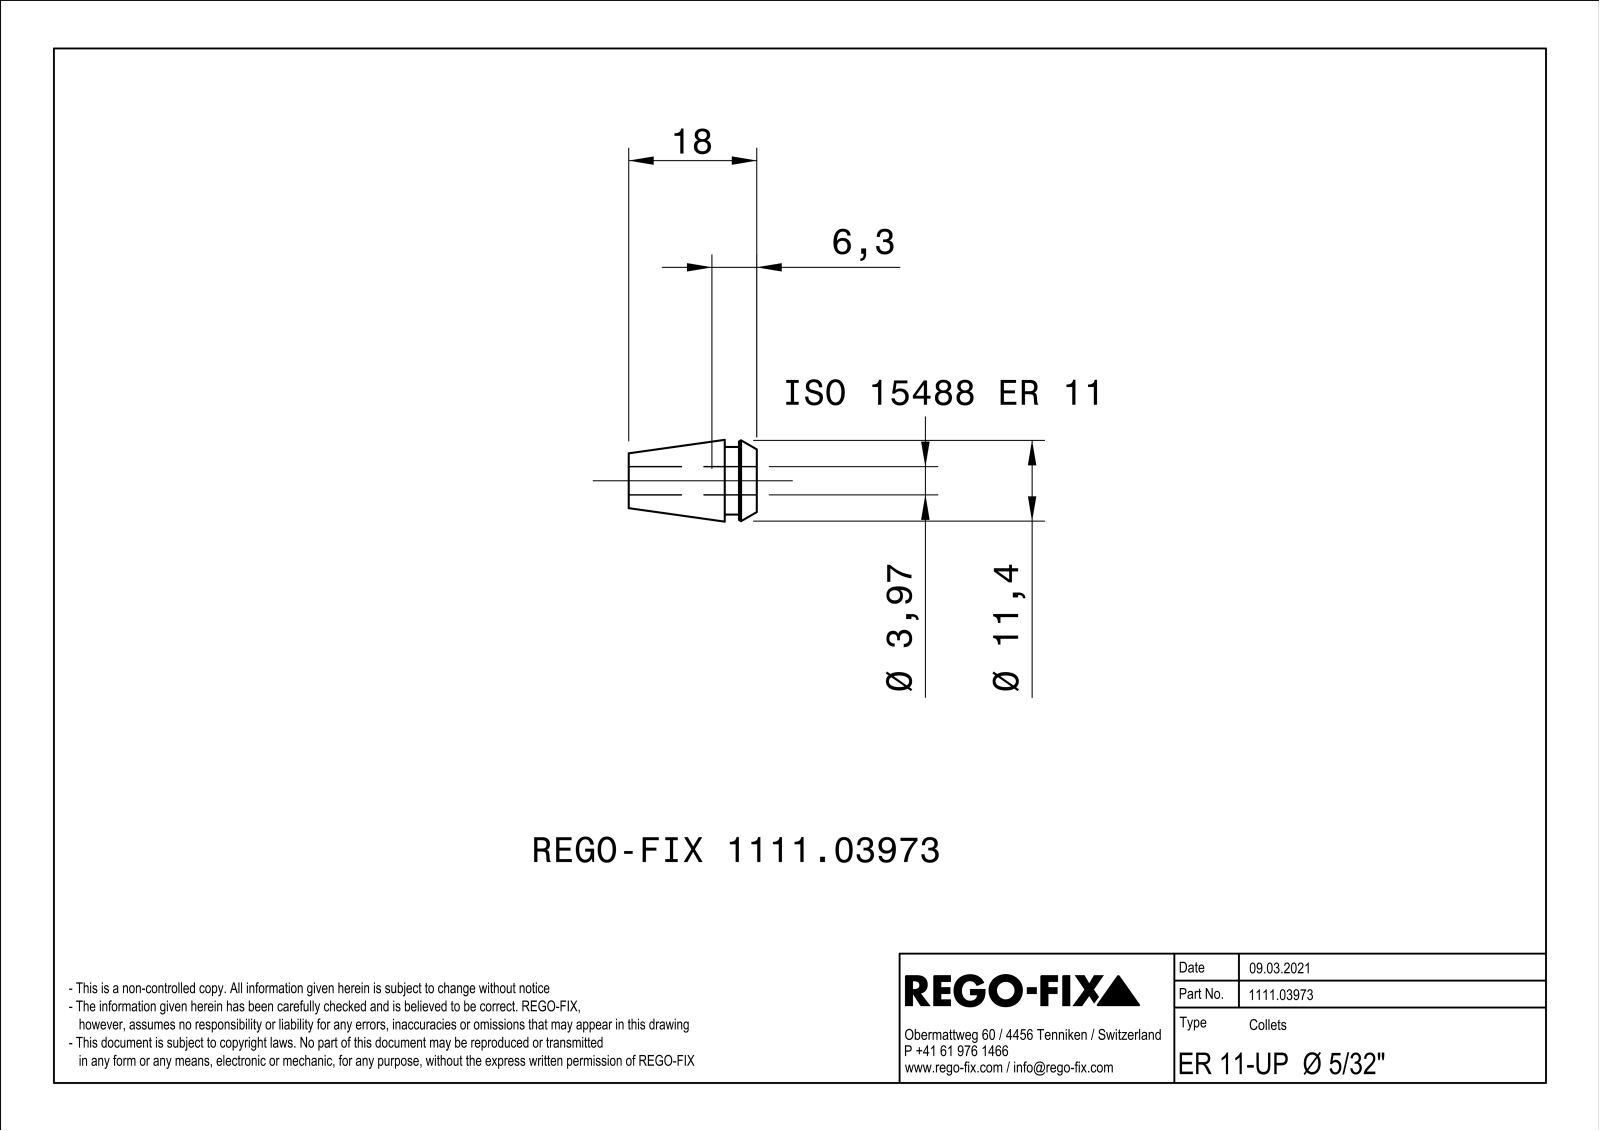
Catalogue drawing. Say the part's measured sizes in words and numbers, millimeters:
The part is named "NOCUT". Its 3-D file was written by "SIEMENS PLM Software Solid Edge ST10 (AUTOMOTIVE_DESIGN)". It is 1 solid with 157 faces: 66 planar, 37 cylindrical and 54 other. Overall it measures 18 by 11.5 by 11.49 millimeters. Its volume is 894 cubic millimeters and its surface area 1 760 square millimeters. Round holes: 1 of diameter 3.97. Round bosses or shafts: 1 of diameter 11.5, 1 of diameter 9.5. Partial cylindrical surfaces (rounded edges, fillets, slot ends): 12 of radius 25. The main face-to-face distances are 0.45, 0.46, 0.44, 2.5, 4.5, 2, 18, 15.5, 13.5, 4.
